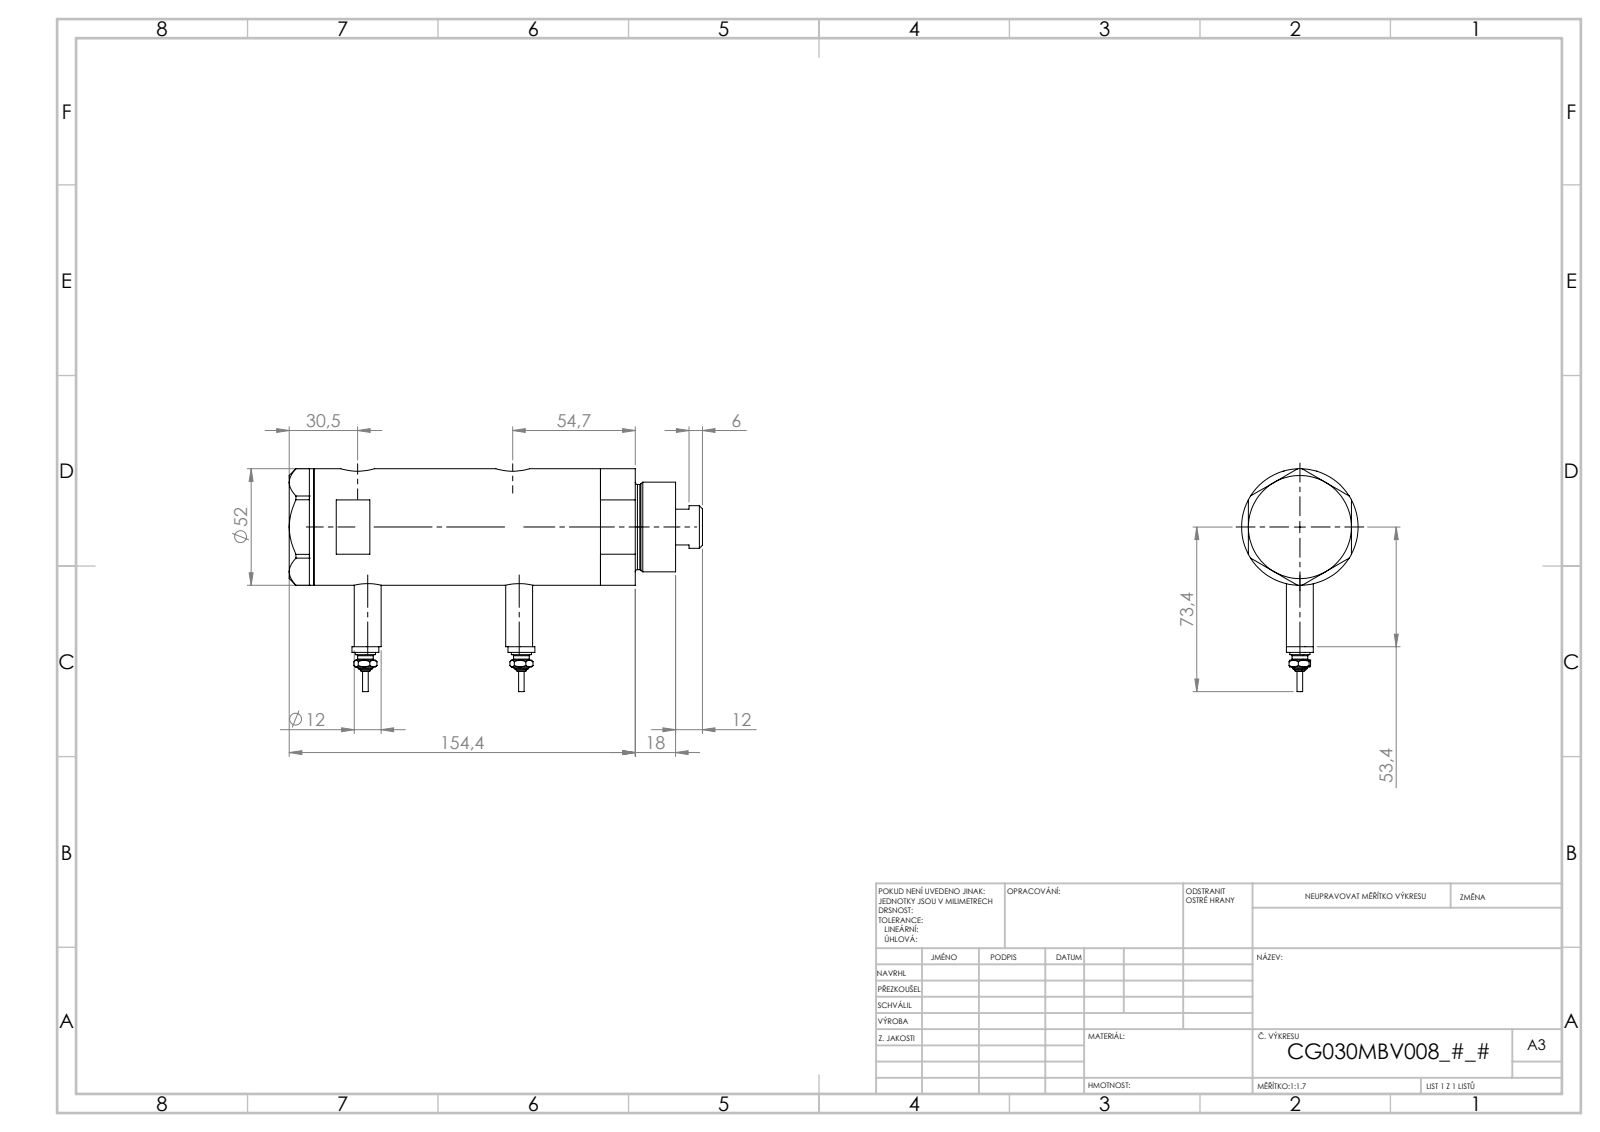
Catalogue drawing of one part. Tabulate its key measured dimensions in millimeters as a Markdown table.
| quantity | value |
| --- | --- |
| part name | V270CG_MIDDLE; V270CG_VC; V270CG_BACK; Switch (+1 more) |
| STEP written by | SolidWorks 2019 (CONFIG_CONTROL_DESIGN) |
| units | millimeters |
| bodies | 6 solids, 226 faces (93 planar, 69 cylindrical, 64 other) |
| overall size | 184.4 × 99.4 × 52 |
| volume | 349 574 mm³ |
| surface area | 80 604 mm² |
| round holes (diameter × count) | 9.73 × 2, 12.5 × 2, 15 × 2, 6.5 × 1, 20 × 1, 21.5 × 1, 30 × 1, 33 × 1, 44 × 1 |
| round bosses / shafts (diameter × count) | 12 × 4, 9 × 2, 7 × 2, 4.5 × 2, 2.5 × 2, 52 × 1, 40 × 1, 38 × 1 |
| main face-to-face distances | 91.5, 23.8, 67.7, 11, 34.8, 102.5, 46, 36.4, 138.9, 127.9 |
| hole center spacings | 2.9, 4.5, 64.7, 67.6, 69.2, 72.1 |
